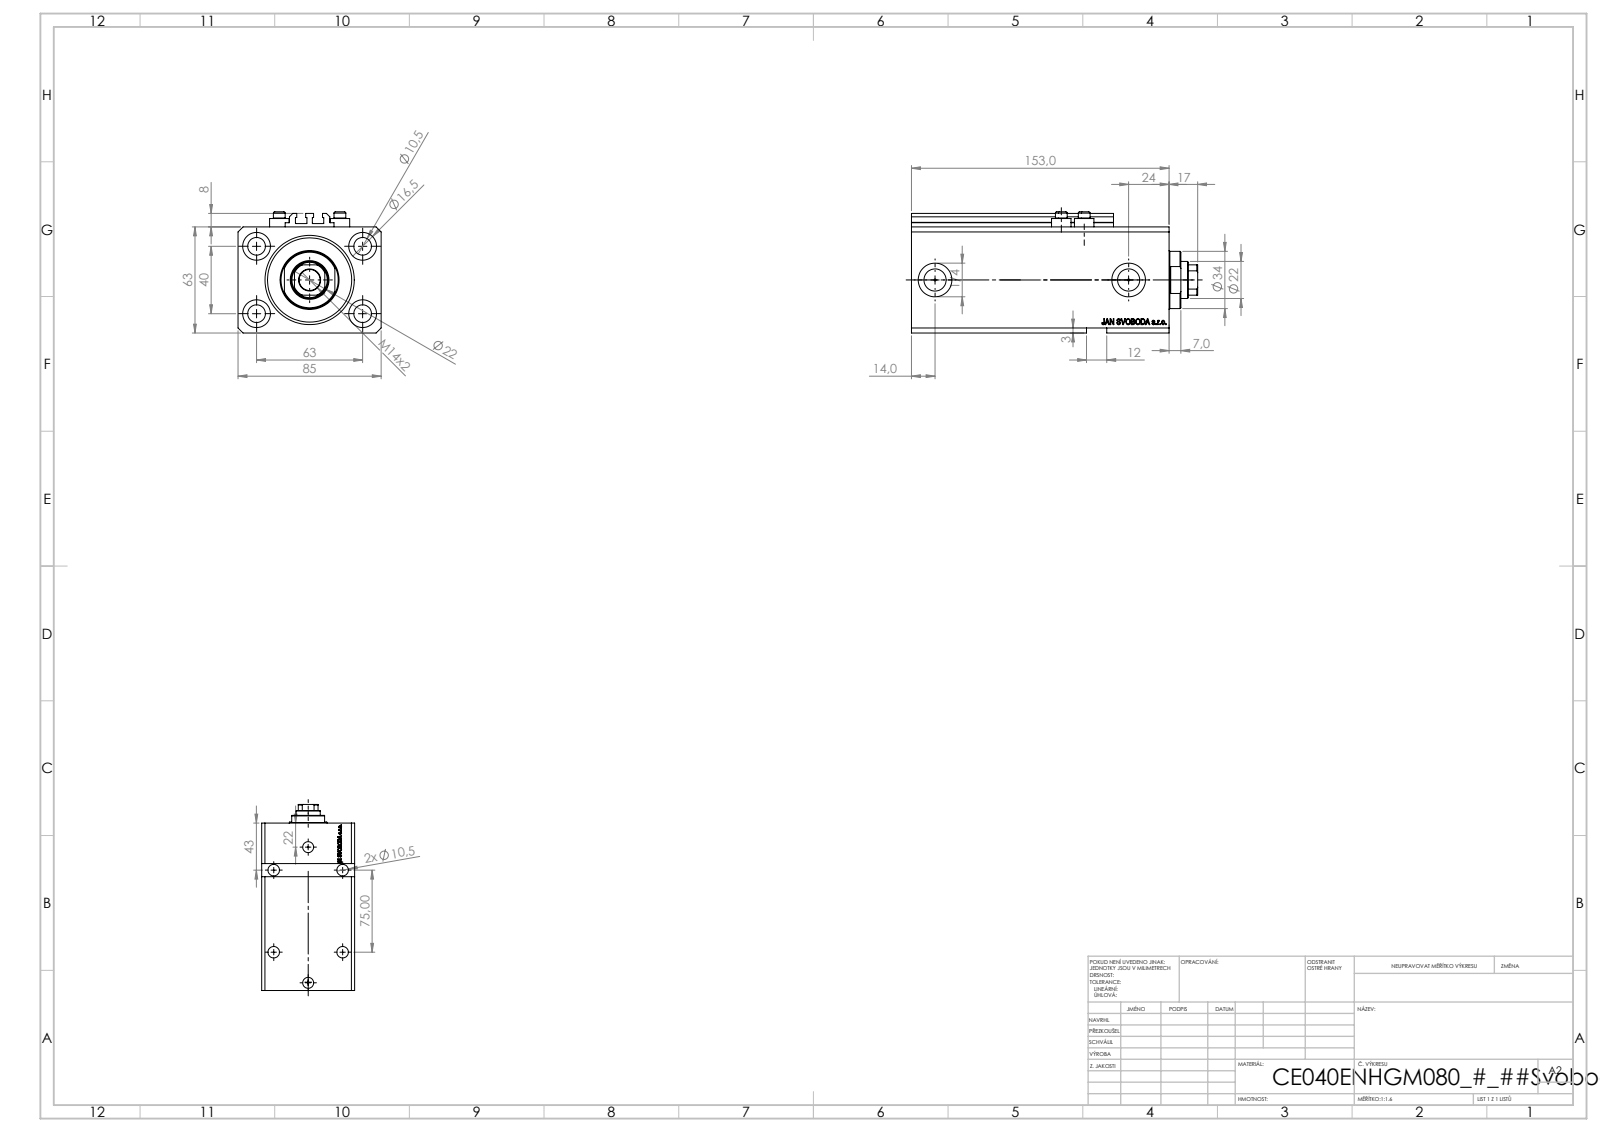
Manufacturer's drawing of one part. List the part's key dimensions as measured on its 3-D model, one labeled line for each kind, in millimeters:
Part name (STEP PRODUCT): V250CE_C_VCP; V250CE_E_Body; V250CE_VC_E; ALLEN BOLT V250CE
STEP written by: SolidWorks 2019 (CONFIG_CONTROL_DESIGN)
Units: millimetres
Bodies: 8 solids, 1107 faces (535 planar, 146 cylindrical, 426 other)
Overall size (bounding box): 170 × 85 × 72
Volume: 683 849 mm³ · Surface area: 140 822 mm²
Round holes (diameter × count): ⌀10.5 ×8, ⌀1.25 ×4, ⌀4 ×4, ⌀16.5 ×4, ⌀10 ×2, ⌀13.16 ×2, ⌀20 ×2, ⌀12.5 ×1, ⌀22 ×1, ⌀40 ×1, ⌀53 ×1
Round bosses / shafts (diameter × count): ⌀11.6 ×4, ⌀7 ×4, ⌀34 ×1
Partial cylindrical surfaces — rounded edges, fillets, slot ends (radius × count): R0.2 ×10, R10.5 ×1
Main face-to-face distances: 63, 85, 153, 17, 136, 11.4, 124.6, 141.6, 3, 65
Hole centre spacings: 37.31, 63, 13.6, 15.4, 24.96, 33.62, 36, 37.86
